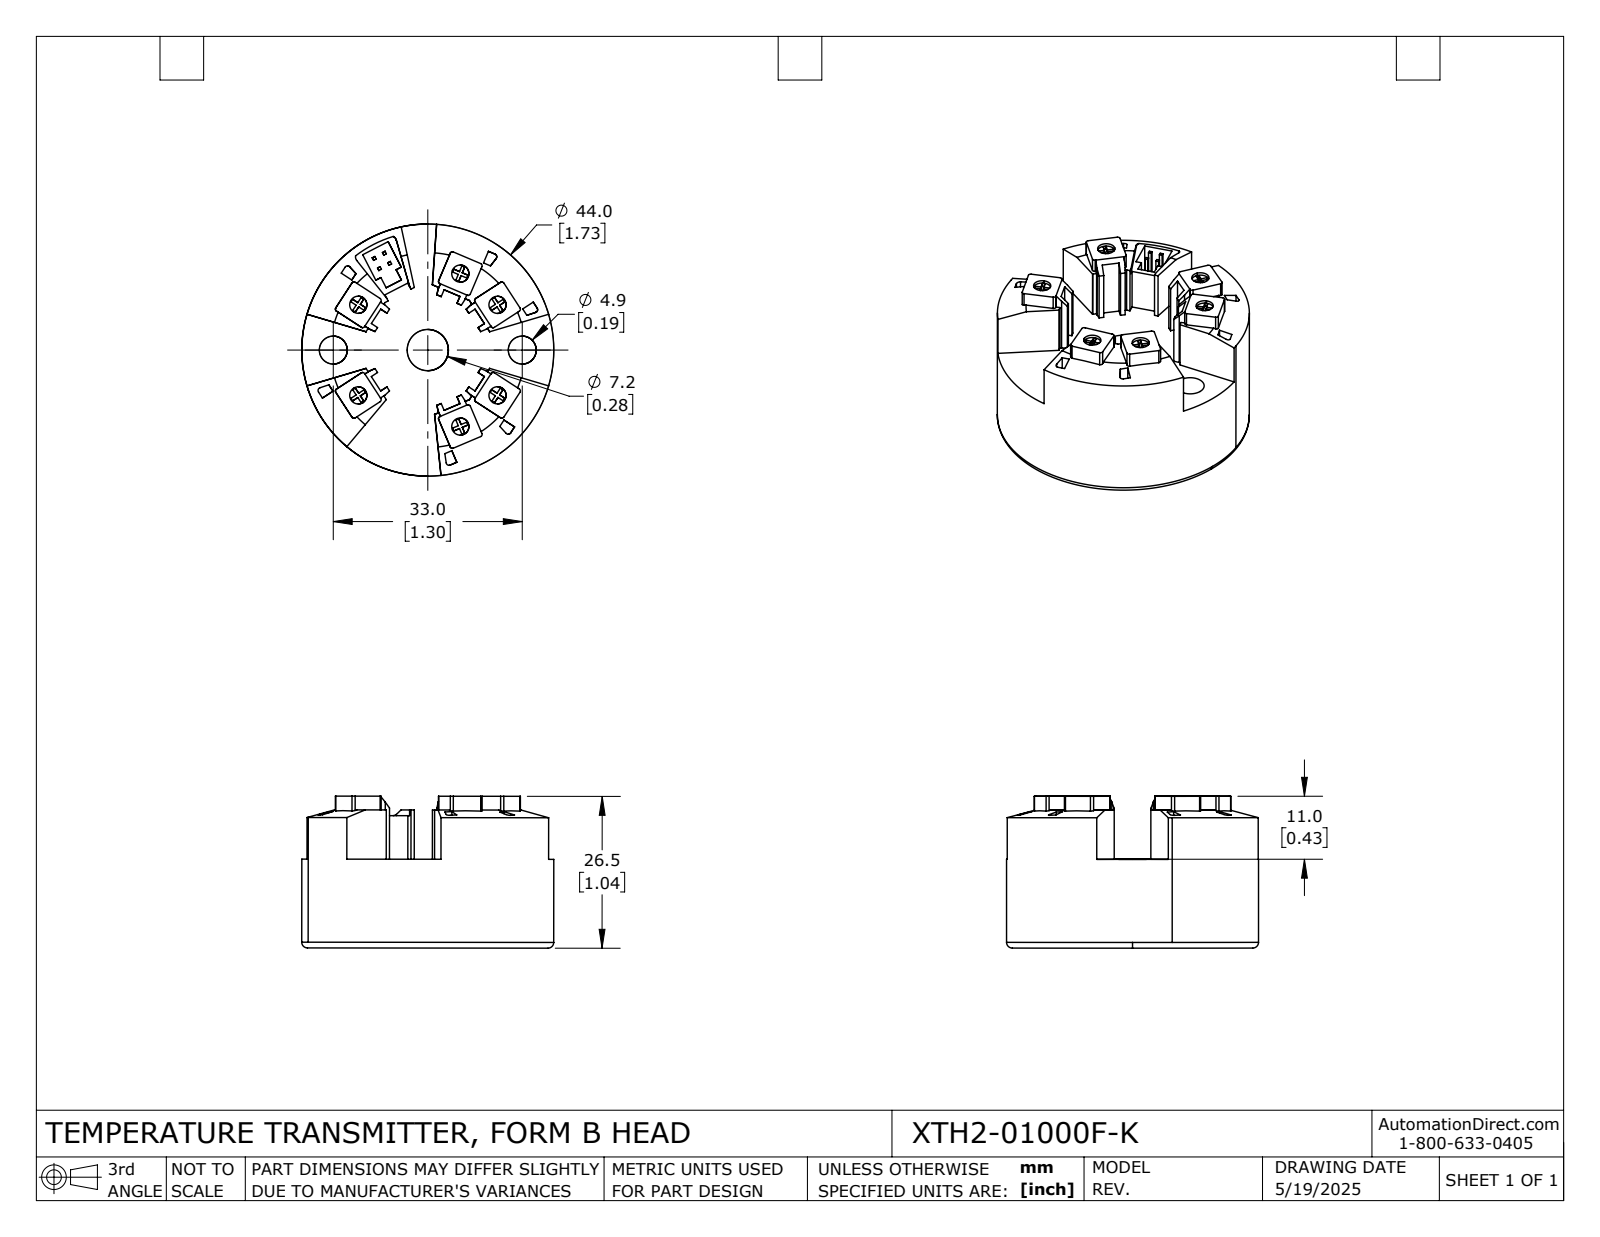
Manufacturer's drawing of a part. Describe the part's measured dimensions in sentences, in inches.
The part is named "XTDH2-01000F-K". Its 3-D file was written by "SolidWorks 2024 (AUTOMOTIVE_DESIGN)". It is 1 solid with 341 faces: 281 planar, 52 cylindrical and 8 other. Overall it measures 1.733 by 1.732 by 1.045 inches. Its volume is 1.748 cubic inches and its surface area 13.46 square inches. Round holes: 6 of diameter 0.118, 2 of diameter 0.193, 1 of diameter 0.283. Round bosses or shafts: 1 of diameter 1.732. Partial cylindrical surfaces (rounded edges, fillets, slot ends): 24 of radius 0.016, 6 of radius 0.02, 2 of radius 0.039. The main face-to-face distances are 0.61, 1.043, 0.433, 0.059, 0.177, 0.039, 0.02, 0.118, 0.949, 0.339. The hole center spacings are 0.571, 0.333, 0.355, 0.356, 0.65, 0.677, 0.733, 0.875.
